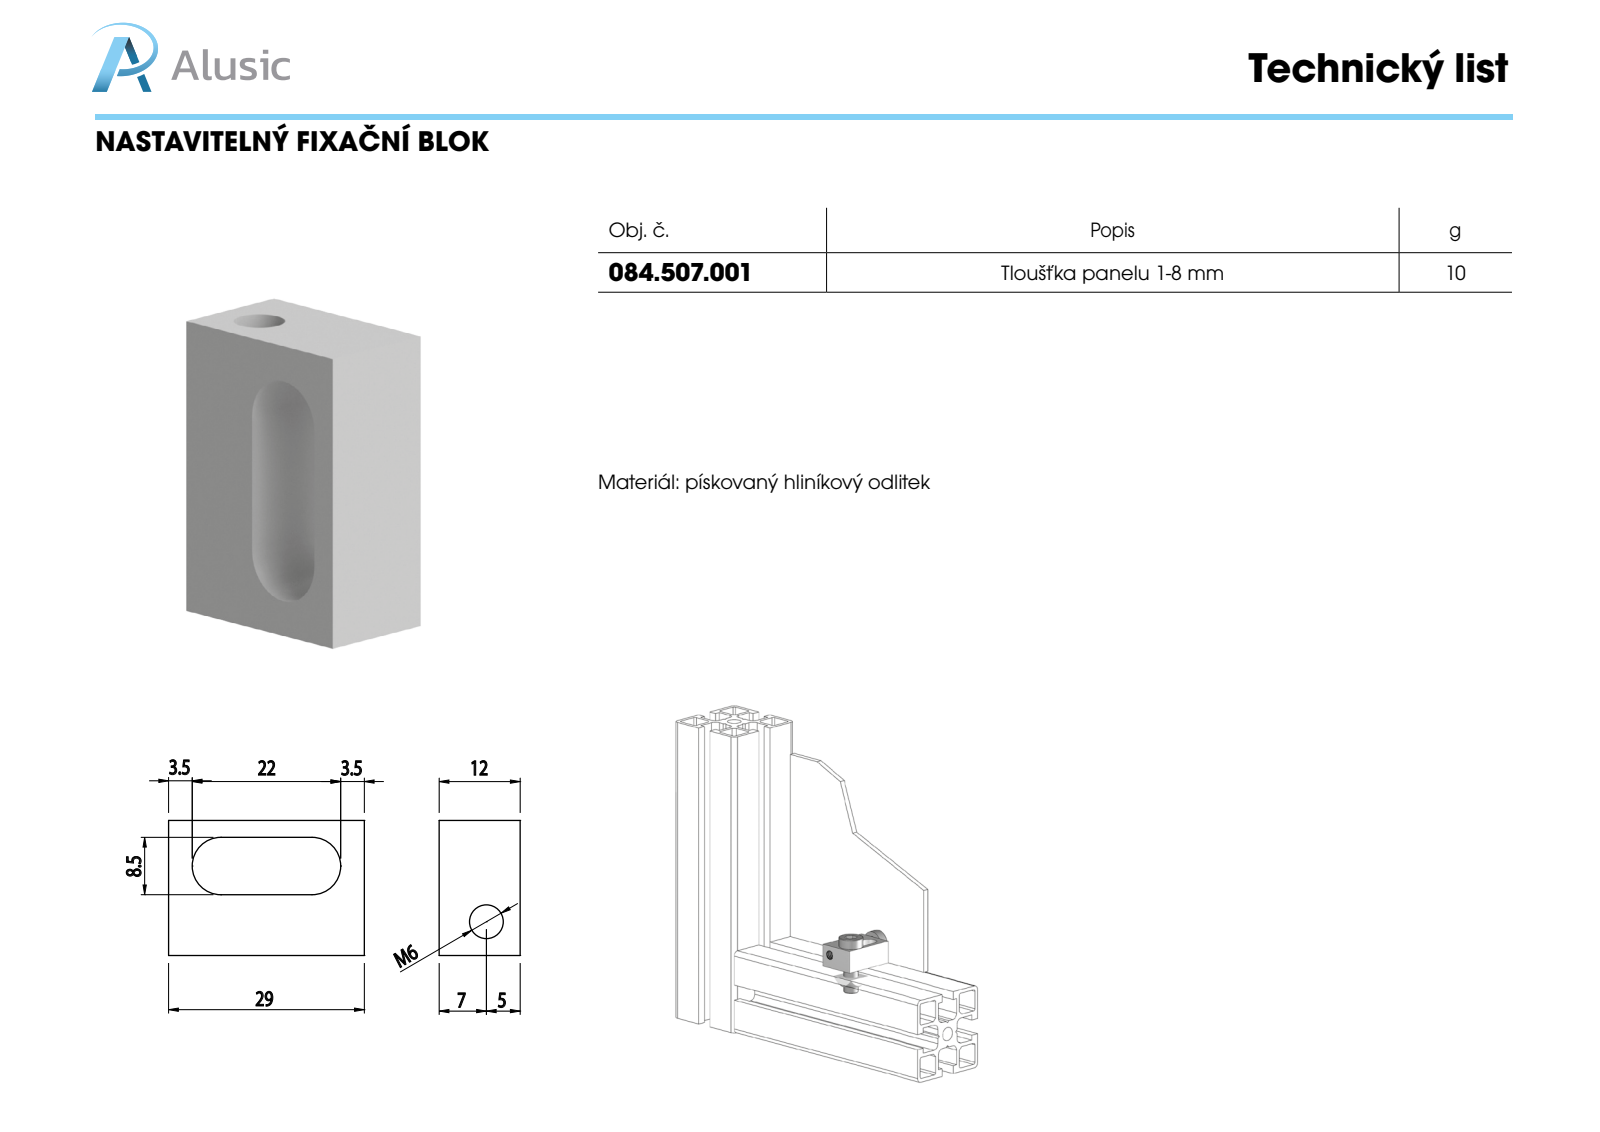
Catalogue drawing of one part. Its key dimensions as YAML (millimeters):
part_name: "084.507.001"
step_written_by: "SolidWorks 2011 (CONFIG_CONTROL_DESIGN)"
units: millimeters
bodies: {solids: 1, faces: 12, planar: 8, cylindrical: 4, other: 0}
overall_size: [29, 20, 12]
volume: 4333
surface_area: 3054
round_holes:
  - {diameter: 5, count: 1}
partial_cylinders:
  - {radius: 4.25, count: 2}
face_to_face_distances: [12, 20, 29, 9, 11, 17.5, 8.5, 2.5]
